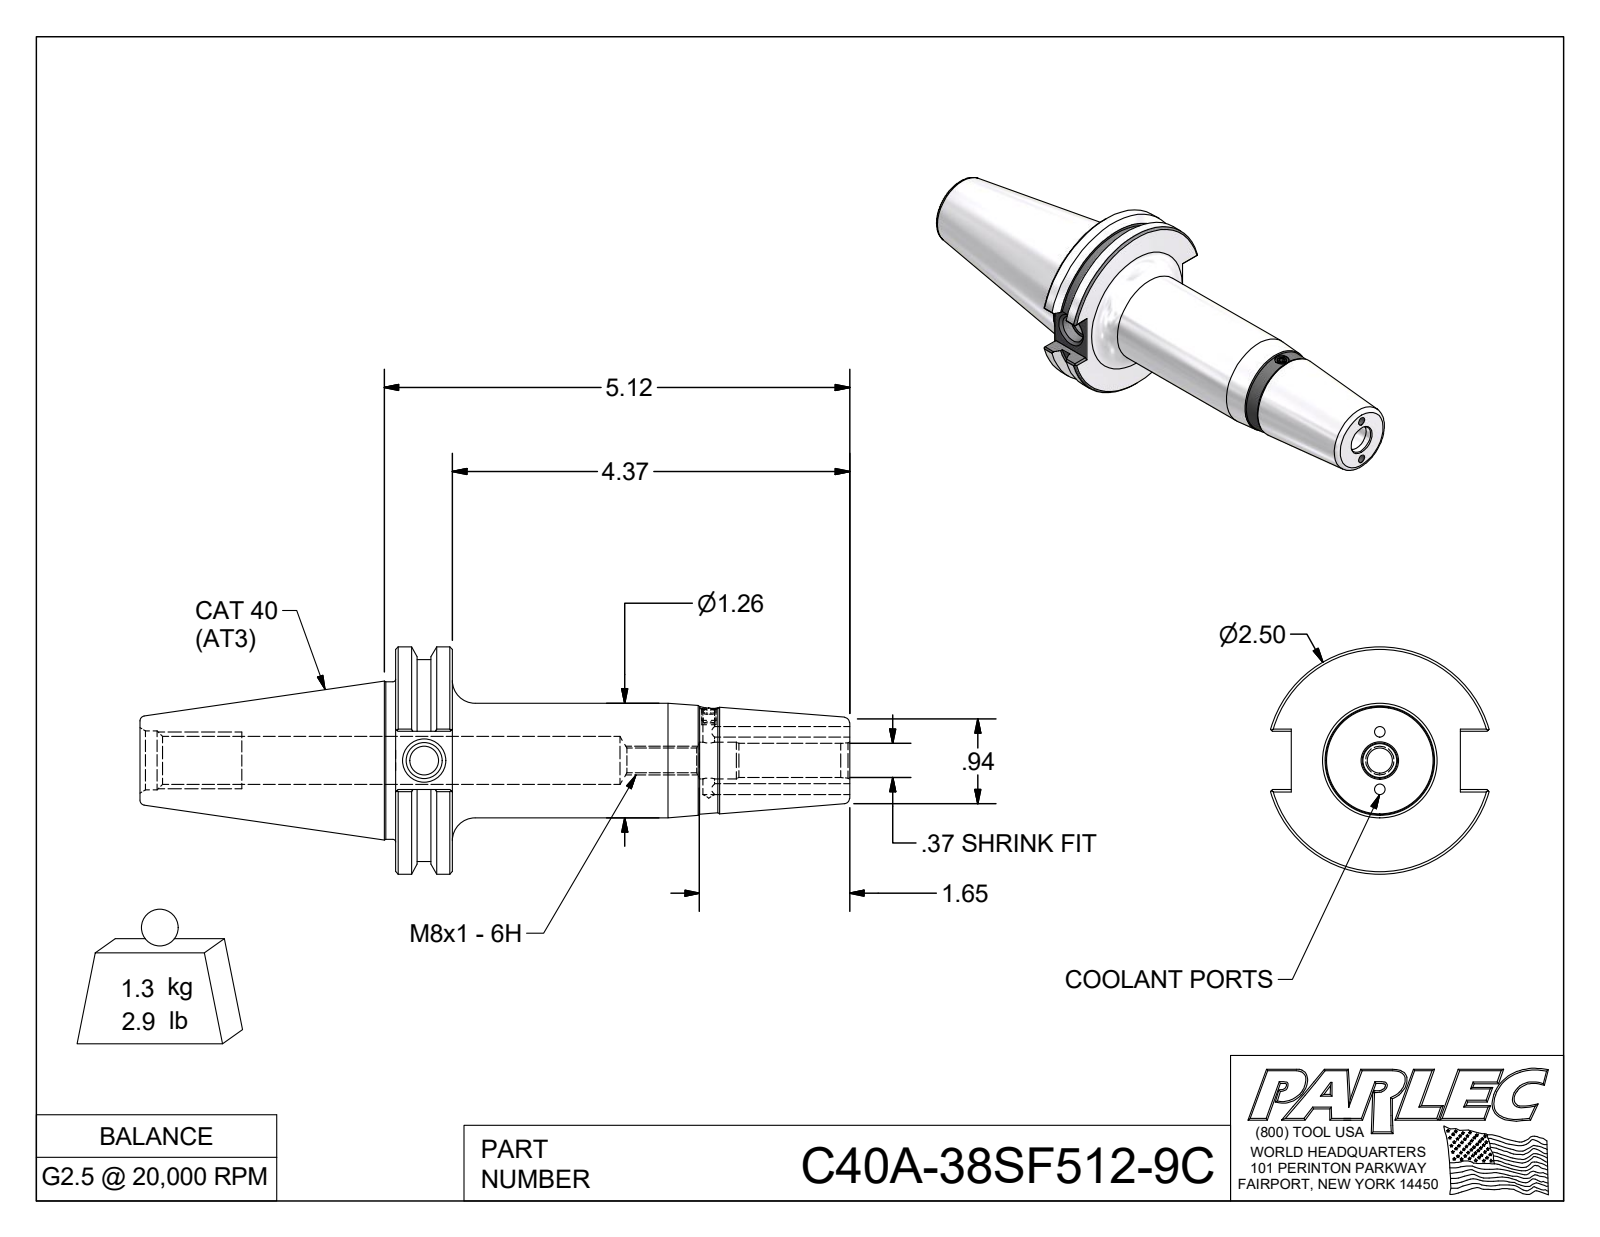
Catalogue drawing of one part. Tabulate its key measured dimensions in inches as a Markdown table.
| quantity | value |
| --- | --- |
| part name | C40A-38SF512-9C; 029-060 |
| STEP written by | Autodesk Inventor 2018 (AUTOMOTIVE_DESIGN) |
| units | inches |
| bodies | 2 solids, 94 faces (41 planar, 21 cylindrical, 32 other) |
| overall size | 7.808 × 2.5 × 2.403 |
| volume | 10.36 in³ |
| surface area | 54.08 in² |
| round holes (diameter × count) | 0.118 × 2, 0.128 × 1, 0.197 × 1, 0.272 × 1, 0.315 × 1, 0.374 × 1, 0.396 × 1, 0.404 × 1, 0.527 × 1, 0.648 × 1 |
| round bosses / shafts (diameter × count) | 2.5 × 1, 2.219 × 1, 1.73 × 1, 1.26 × 1, 0.157 × 1 |
| main face-to-face distances | 0.625, 4.995, 4.37, 0.64, 1.86, 2.812, 3.437, 7.807, 3.201, 0.389 |
| hole center spacings | 0.315, 0.63 |
